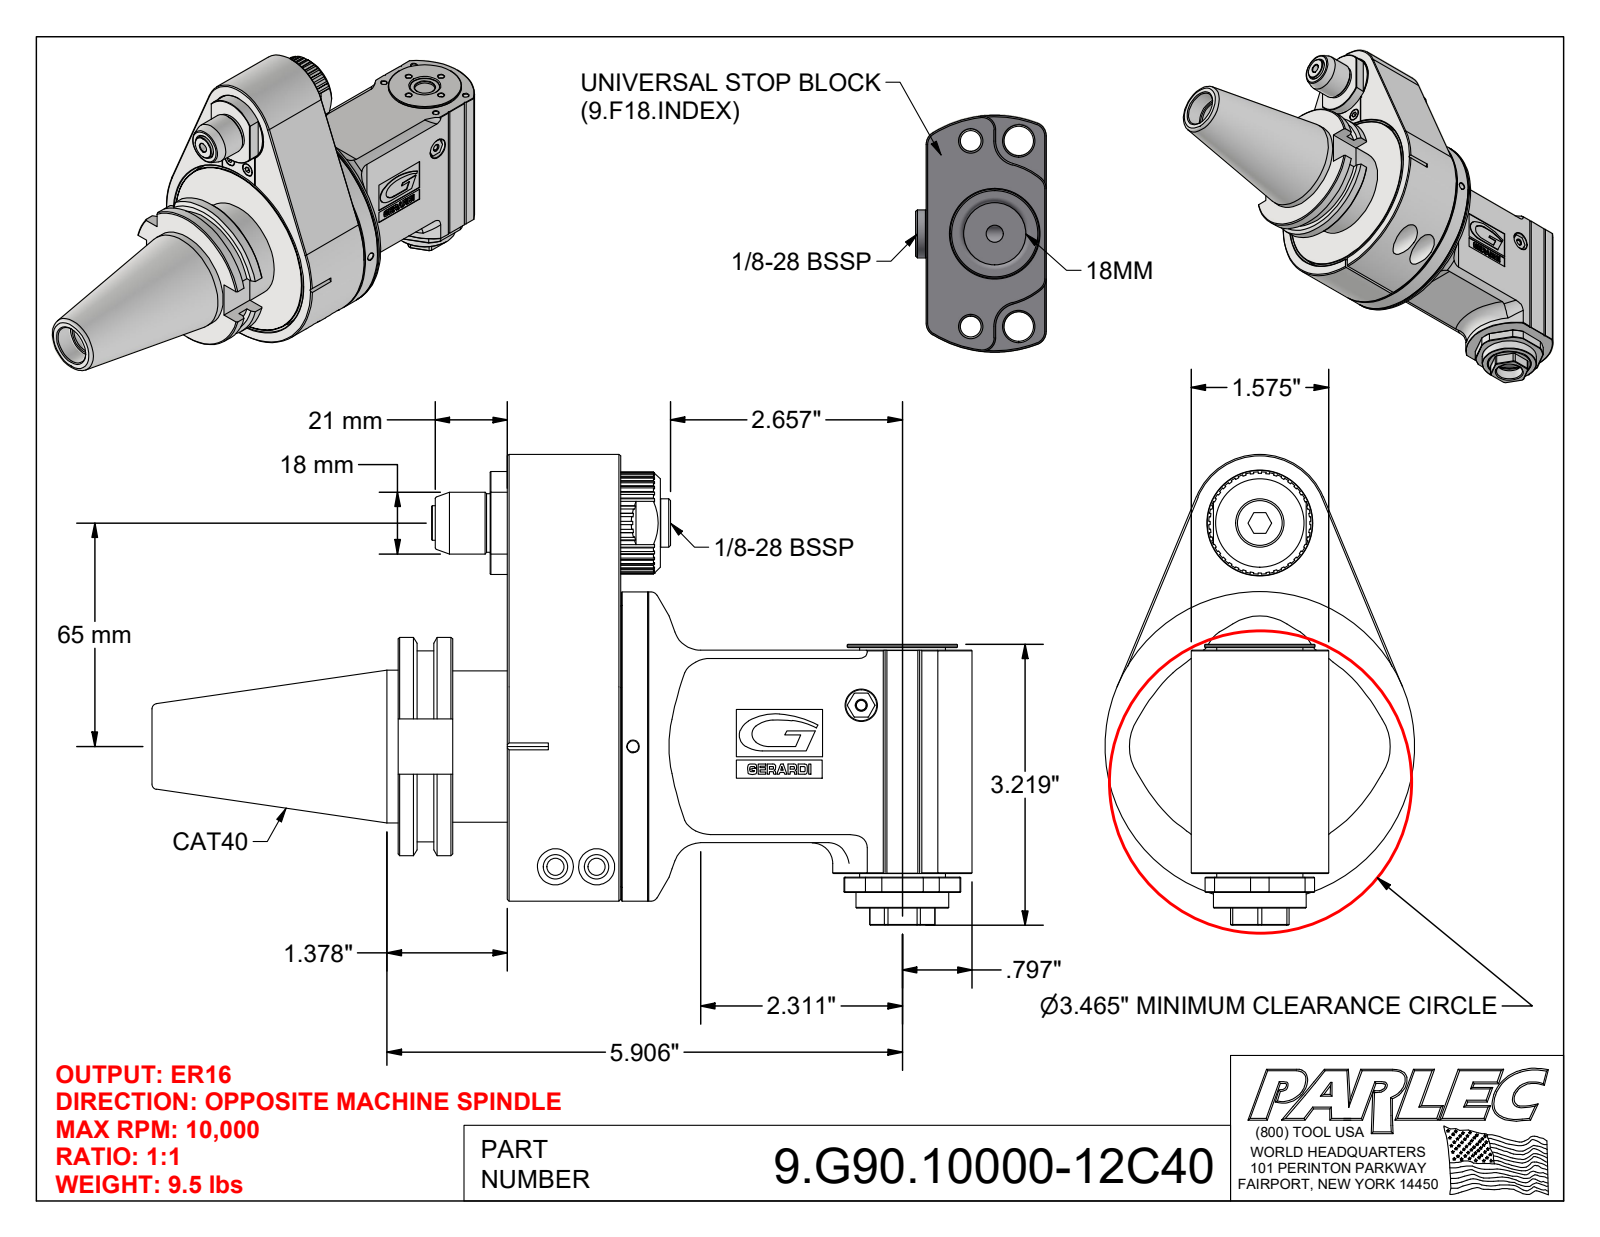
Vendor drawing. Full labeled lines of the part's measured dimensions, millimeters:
Part name (STEP PRODUCT): 9.G90.10000-12C40; 9_GA1_146_1 (Classic, Type 1, Cat40, 65mm); 9_G90_10000
STEP written by: Autodesk Inventor 2022 (AUTOMOTIVE_DESIGN)
Units: millimetres
Bodies: 4 solids, 809 faces (429 planar, 180 cylindrical, 200 other)
Overall size (bounding box): 238.7 × 137 × 90
Volume: 677 400 mm³ · Surface area: 117 900 mm²
Round holes (diameter × count): ⌀4.2 ×6, ⌀2.5 ×4, ⌀2.7 ×4, ⌀5 ×4, ⌀4 ×2, ⌀6 ×2, ⌀7 ×2, ⌀8.5 ×2, ⌀9 ×2, ⌀10.5 ×2, ⌀14 ×2, ⌀18 ×2
Round bosses / shafts (diameter × count): ⌀10 ×2, ⌀90 ×1, ⌀82 ×1, ⌀78 ×1, ⌀55.5 ×1, ⌀44.5 ×1, ⌀44 ×1, ⌀32 ×1
Partial cylindrical surfaces — rounded edges, fillets, slot ends (radius × count): R8 ×4, R2.2 ×2, R25 ×2, R2 ×1, R2.5 ×1, R2.9 ×1, R3.8 ×1, R4 ×1
Main face-to-face distances: 33, 8, 25, 5, 3, 30, 40, 15.9, 39.8, 65
Hole centre spacings: 37.5, 18.5, 64.9, 10, 11, 14.1, 16, 19.4
